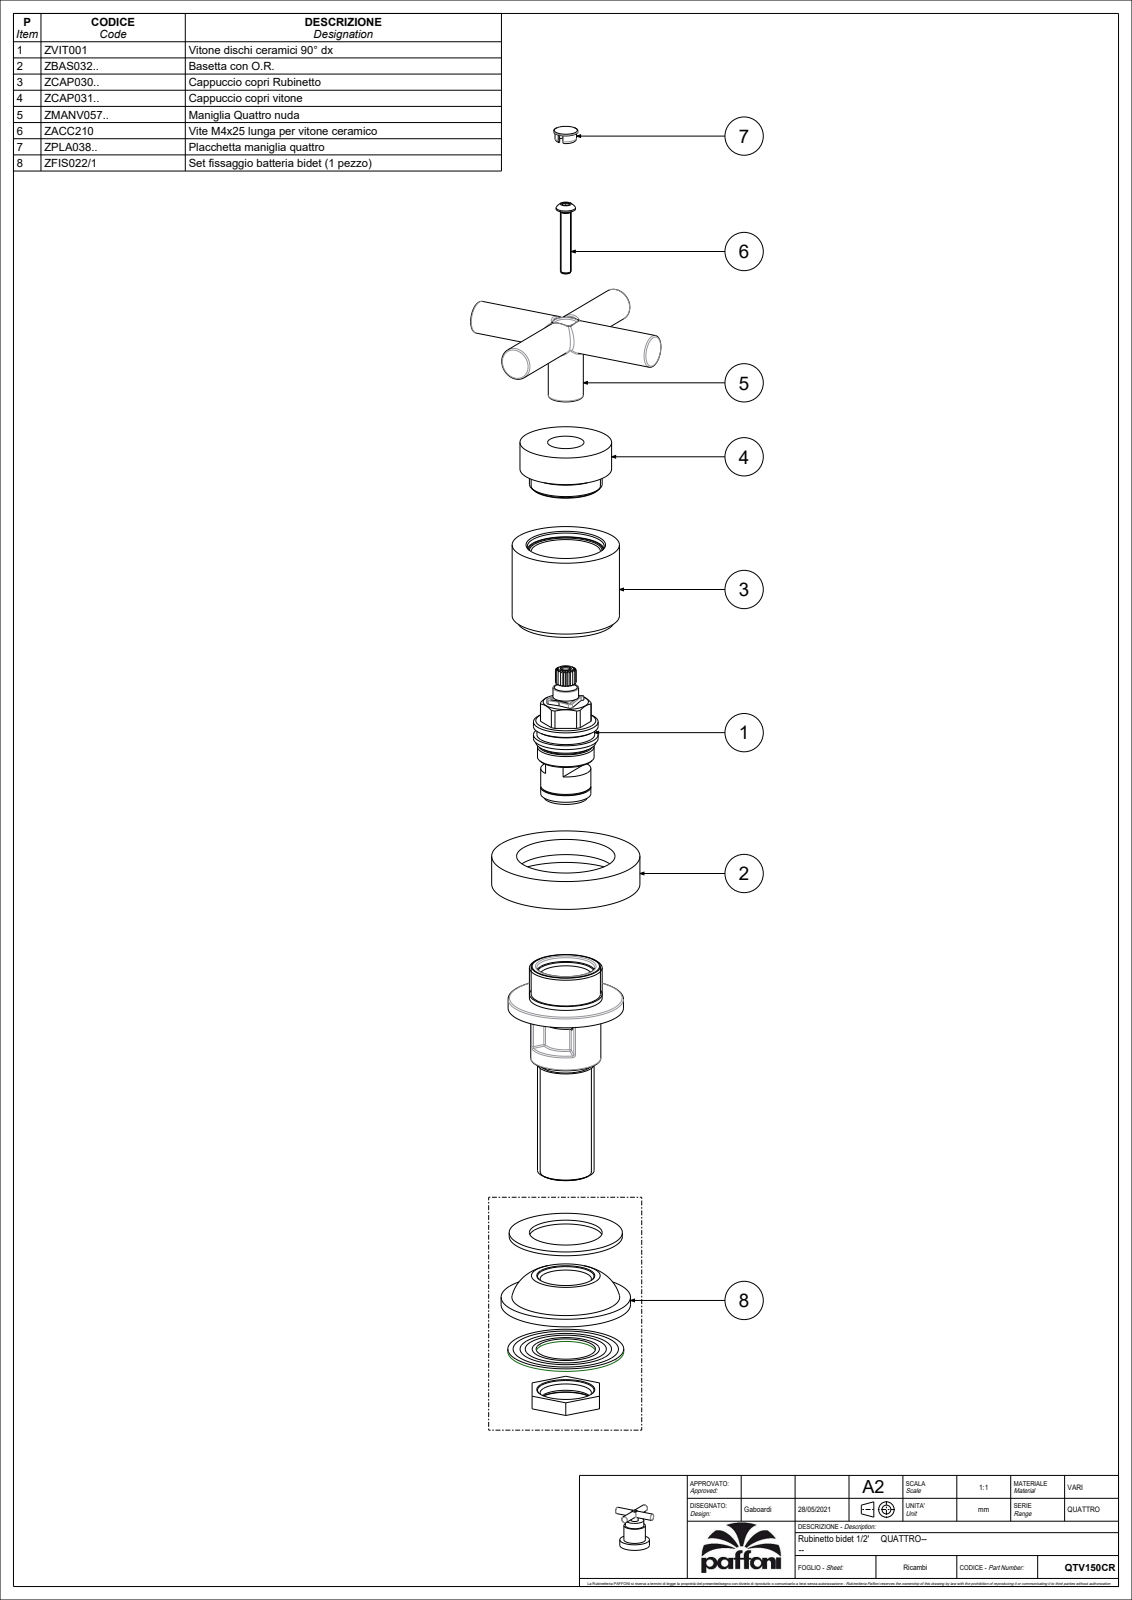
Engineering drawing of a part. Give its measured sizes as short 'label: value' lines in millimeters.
name: QTV150CR
written by: CREO PARAMETRIC BY PTC INC, 2020044 (CONFIG_CONTROL_DESIGN)
unit: mm
bodies: 2 solids, 392 faces (190 planar, 105 cylindrical, 97 other)
size: 75 × 75 × 68.7
volume: 76 890 mm³; area: 27 384 mm²
holes: 1× ⌀3.3, 1× ⌀4.5, 1× ⌀7, 1× ⌀8, 1× ⌀8.8, 1× ⌀9.5, 1× ⌀13.5, 1× ⌀18.6, 1× ⌀19, 1× ⌀20, 1× ⌀22, 1× ⌀25.7
bosses: 2× ⌀12, 1× ⌀55, 1× ⌀49, 1× ⌀42.8, 1× ⌀39.8, 1× ⌀34, 1× ⌀24, 1× ⌀21.4
rounds: 17× R0.1, 10× R0.5, 2× R1, 1× R3, 1× R9.4, 1× R13
face distances: 10, 1, 11, 38.5, 49.5, 48.5, 5, 44.5, 4, 32
